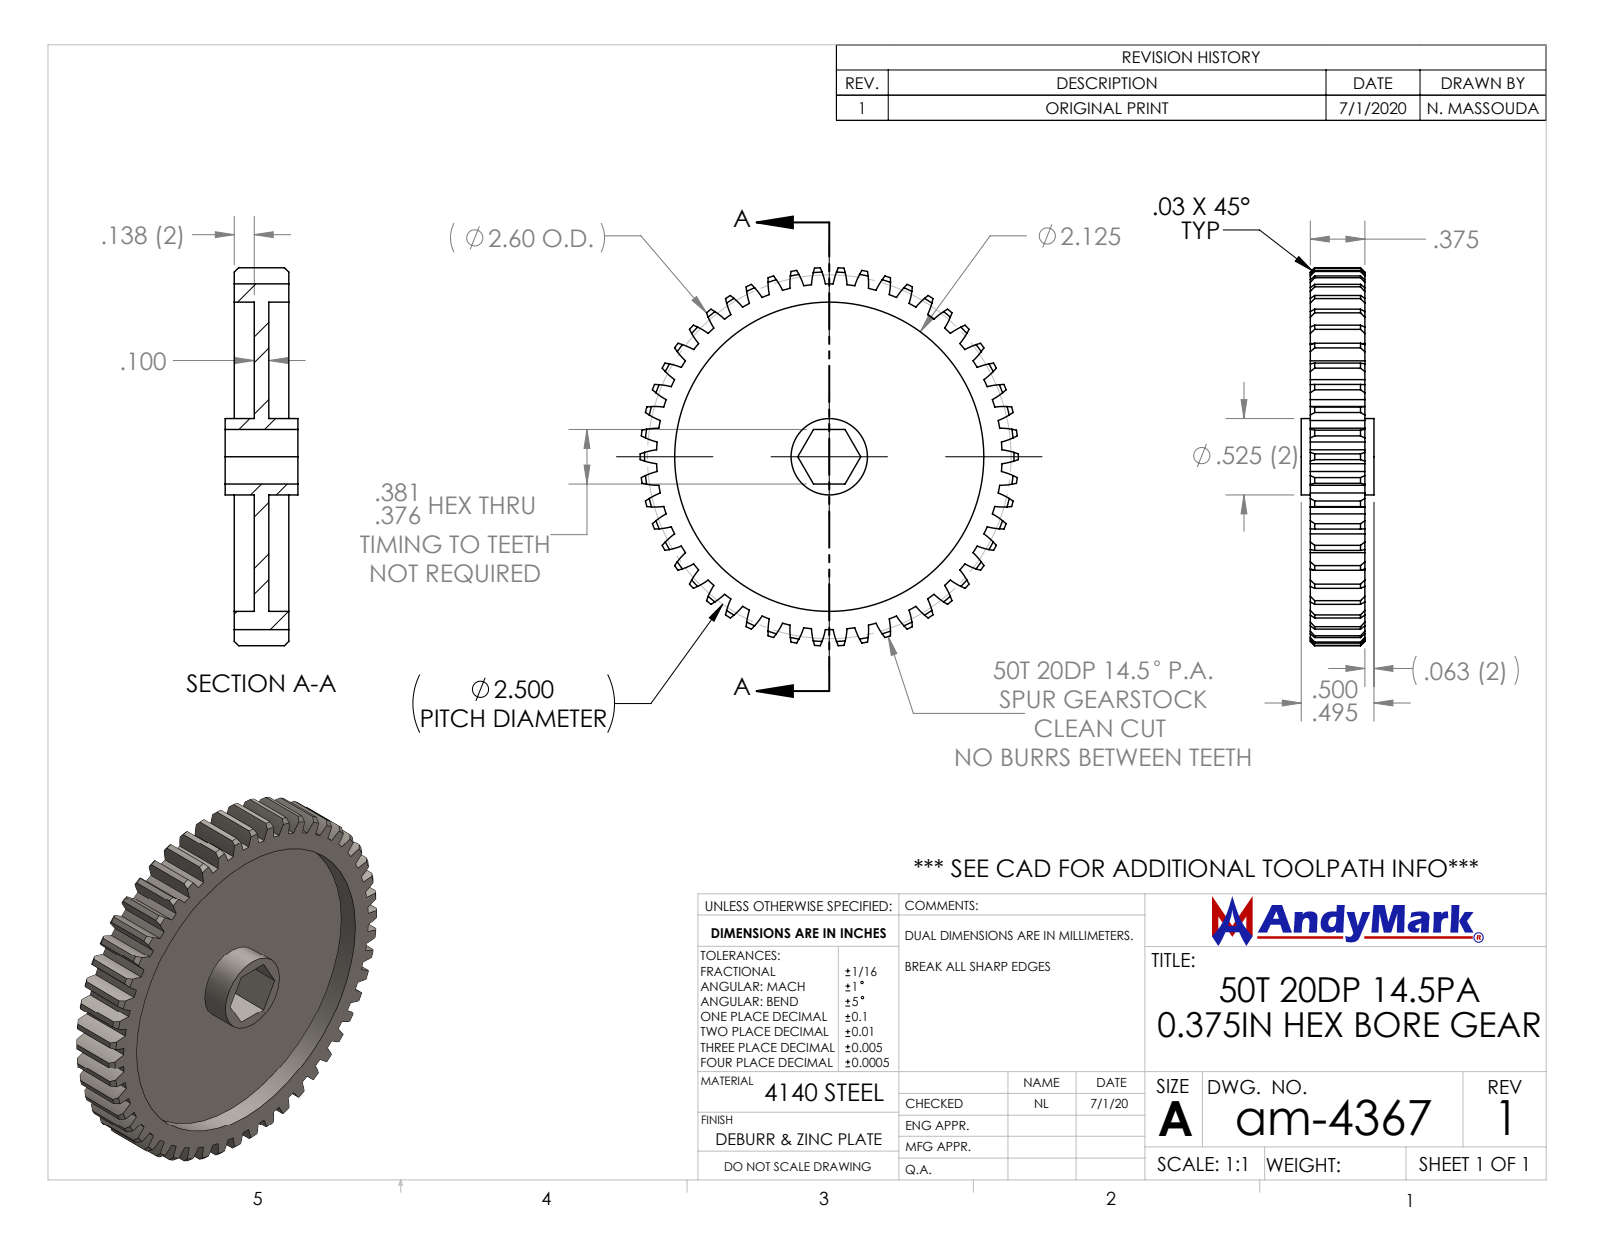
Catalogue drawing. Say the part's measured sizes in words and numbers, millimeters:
The part is named "am-4367 50T 20DP 375hex 375 FW". Its 3-D file was written by "SolidWorks 2019 (CONFIG_CONTROL_DESIGN)". It is 1 solid with 325 faces: 12 planar, 213 cylindrical and 100 other. Overall it measures 66 by 66 by 12.7 millimeters. Its volume is 14 100 cubic millimeters and its surface area 11 970 square millimeters. Round holes: 1 of diameter 54. Round bosses or shafts: 1 of diameter 13.3. Partial cylindrical surfaces (rounded edges, fillets, slot ends): 100 of radius 12.7, 1 of radius 30.2, 1 of radius 33. The main face-to-face distances are 2.5, 3.5, 6, 9.5, 6, 3.5, 9.5, 5.1, 7.6, 1.6.
